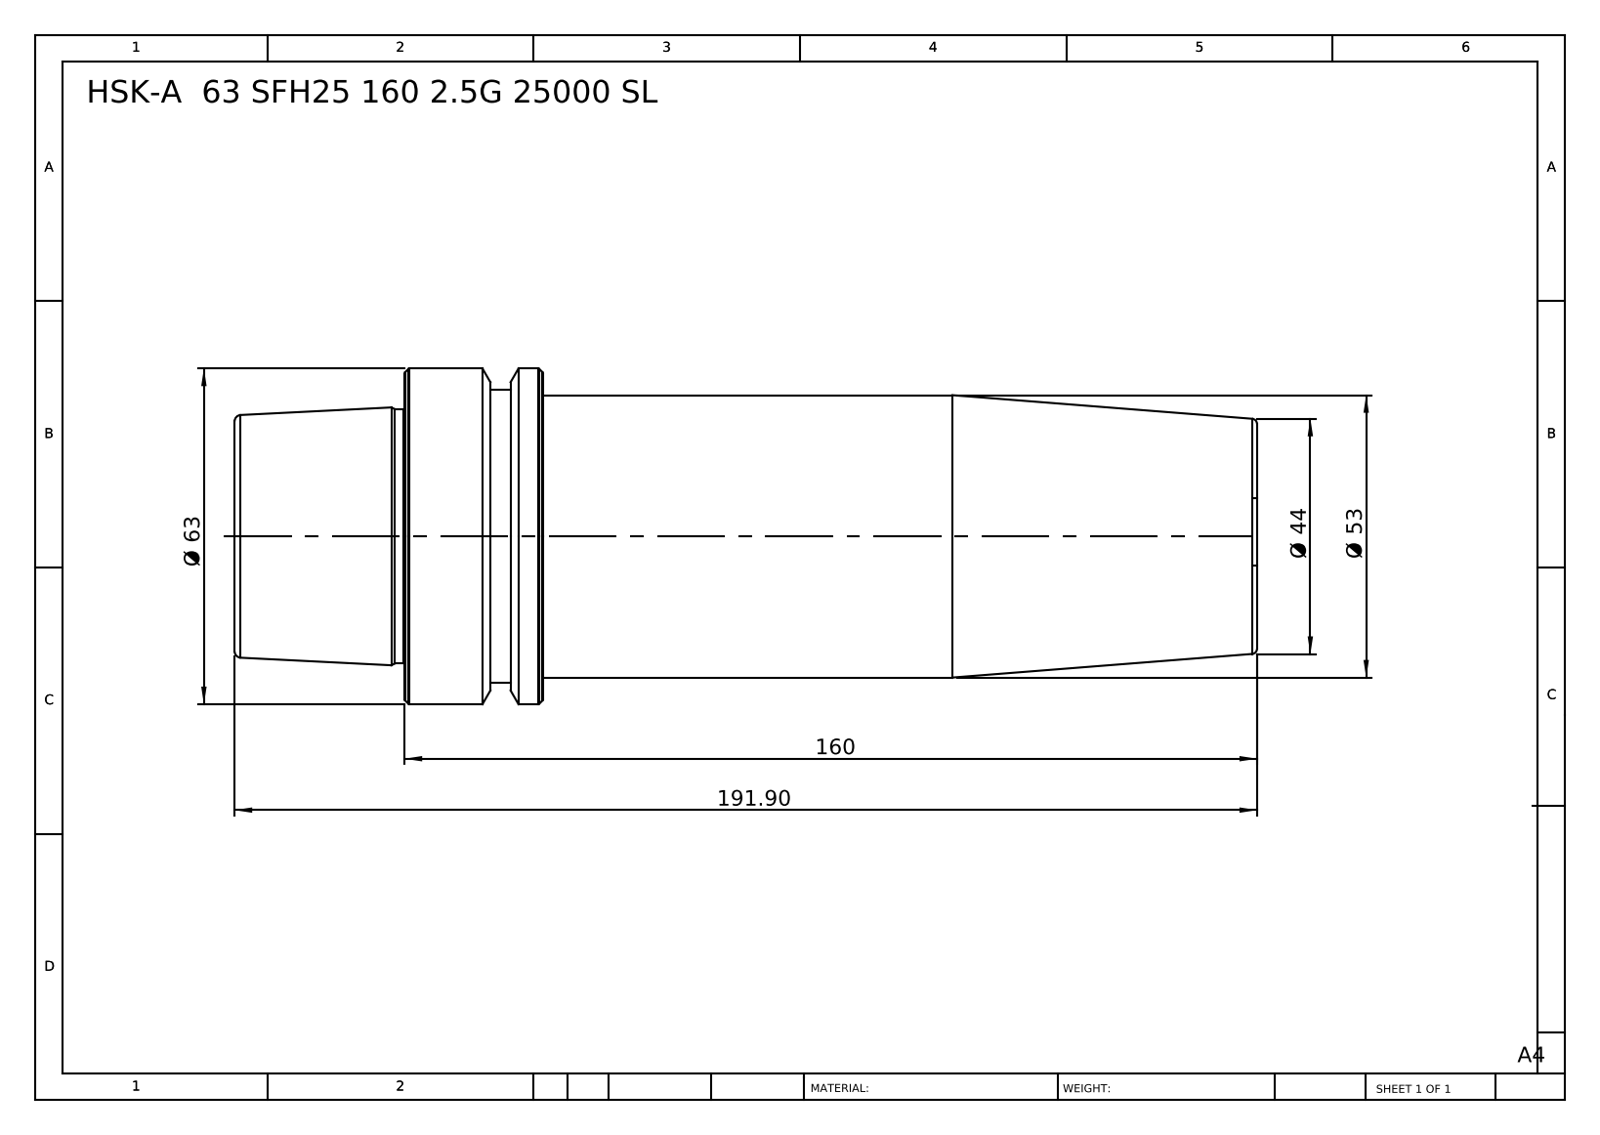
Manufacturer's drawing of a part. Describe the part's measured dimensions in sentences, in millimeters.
The part is named "HSK-A 63 SFH25 160 2.5G 25000 SL". Its 3-D file was written by "SolidWorks 2014 (CONFIG_CONTROL_DESIGN)". It is 1 solid with 46 faces: 6 planar, 10 cylindrical and 30 other. Overall it measures 191.9 by 63 by 63 millimeters. Its volume is 407 992 cubic millimeters and its surface area 37 444 square millimeters. Round bosses or shafts: 1 of diameter 63, 1 of diameter 55, 1 of diameter 53, 1 of diameter 47.78. The main face-to-face distances are 191.9, 134, 57.9, 160, 26, 31.9, 140.1, 6.1, 19.9, 51.8.
